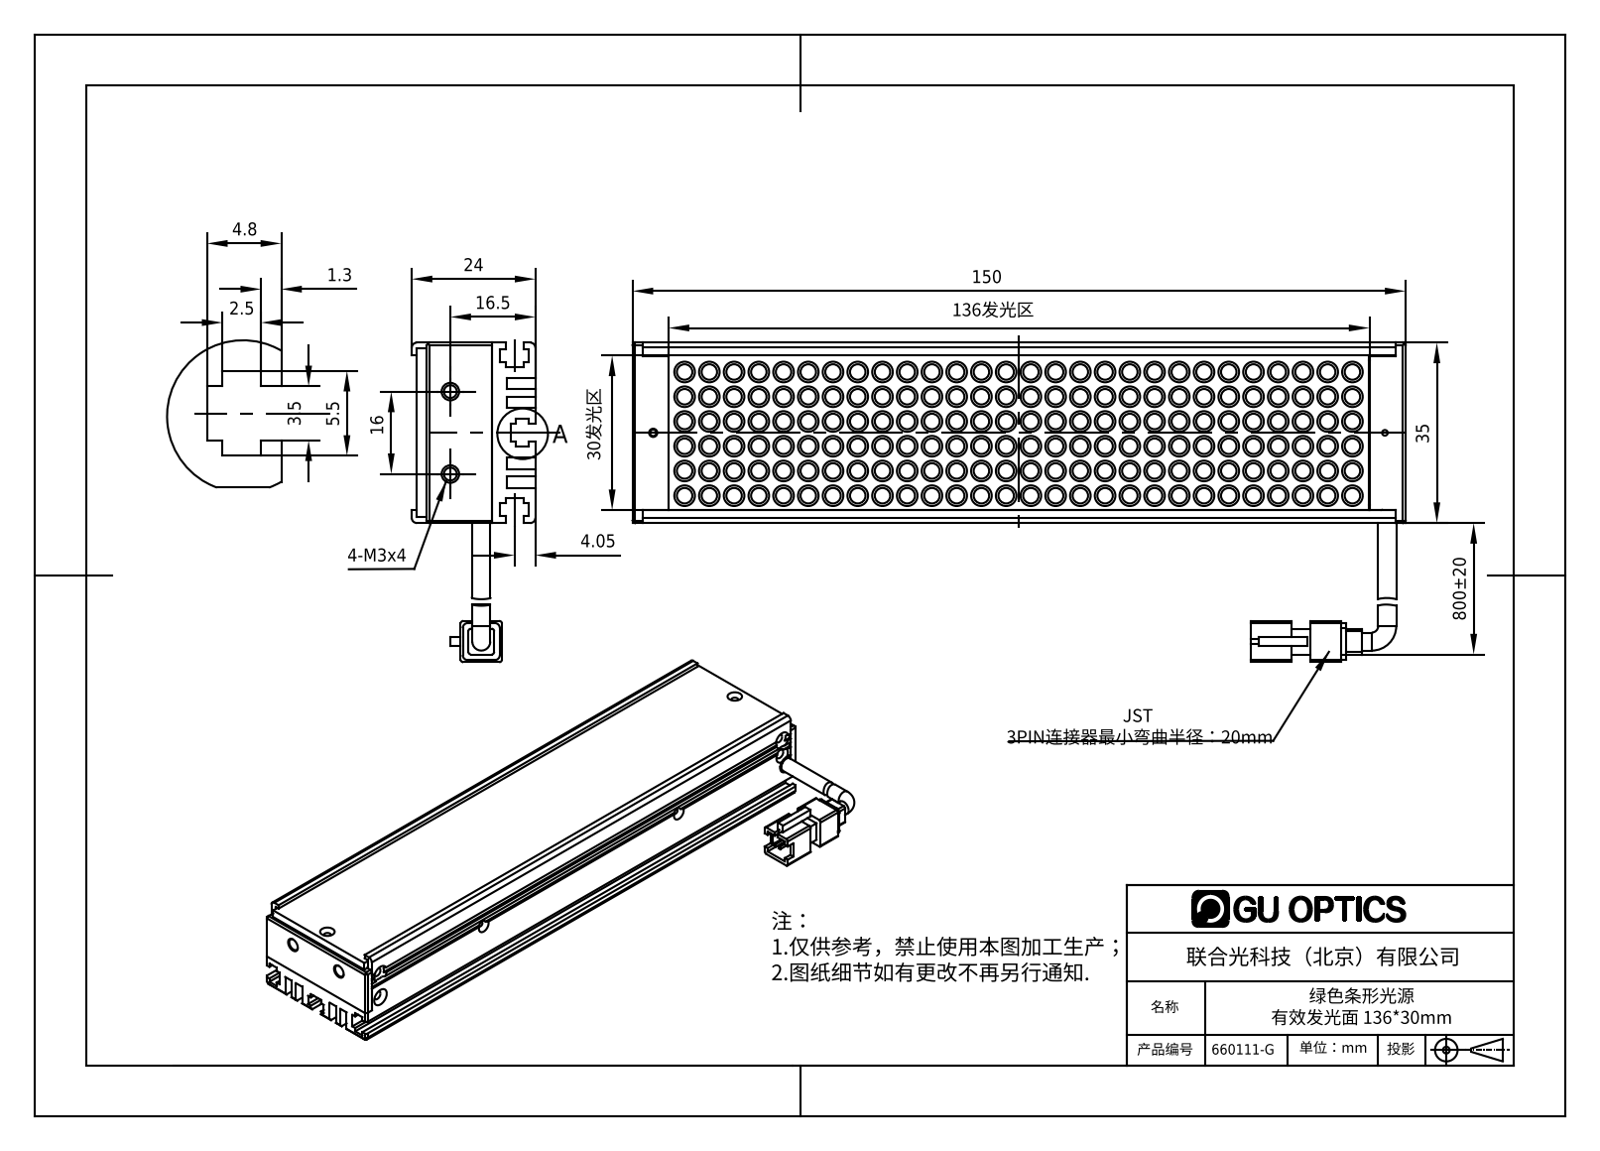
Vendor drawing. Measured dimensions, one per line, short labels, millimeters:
name: 660111-G
written by: SolidWorks 2016 (AUTOMOTIVE_DESIGN)
unit: mm
bodies: 8 solids, 1543 faces (480 planar, 765 cylindrical, 298 other)
size: 150 × 62 × 24
volume: 66 196 mm³; area: 68 375 mm²
holes: 5× ⌀1.6, 4× ⌀1.25, 4× ⌀2.2, 2× ⌀1.7, 2× ⌀2.5, 2× ⌀3, 1× ⌀2.4
bosses: 168× ⌀4, 168× ⌀3, 2× ⌀3.5
rounds: 12× R1, 8× R0.5, 1× R1.65
face distances: 12, 8.5, 2, 3.5, 10.5, 14, 1, 2.5, 3.7, 15.5
hole spacings: 7, 36.17, 104.06, 140, 2.5, 4.5, 16, 36
